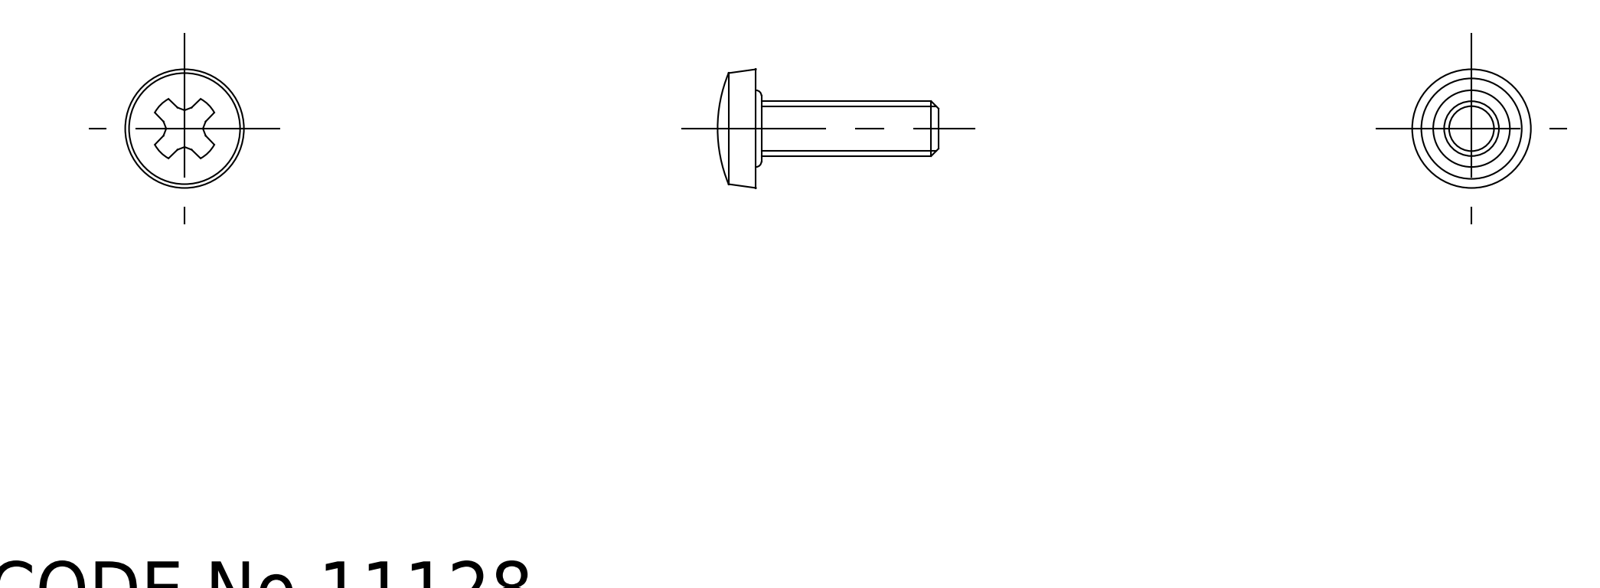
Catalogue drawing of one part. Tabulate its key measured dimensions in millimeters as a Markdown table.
| quantity | value |
| --- | --- |
| part name | screw; TL_417_M3_10 |
| STEP written by | SolidWorks 2015 (AUTOMOTIVE_DESIGN) |
| units | millimeters |
| bodies | 2 solids, 38 faces (20 planar, 8 cylindrical, 10 other) |
| overall size | 12.04 × 6.5 × 6.5 |
| volume | 119 mm³ |
| surface area | 223 mm² |
| round holes (diameter × count) | 5.5 × 1 |
| round bosses / shafts (diameter × count) | 3 × 1 |
| partial cylindrical surfaces (radius × count) | 1.85 × 1 |
| main face-to-face distances | 1, 1.3, 11.3, 10.3, 10, 1.12, 1.88 |
